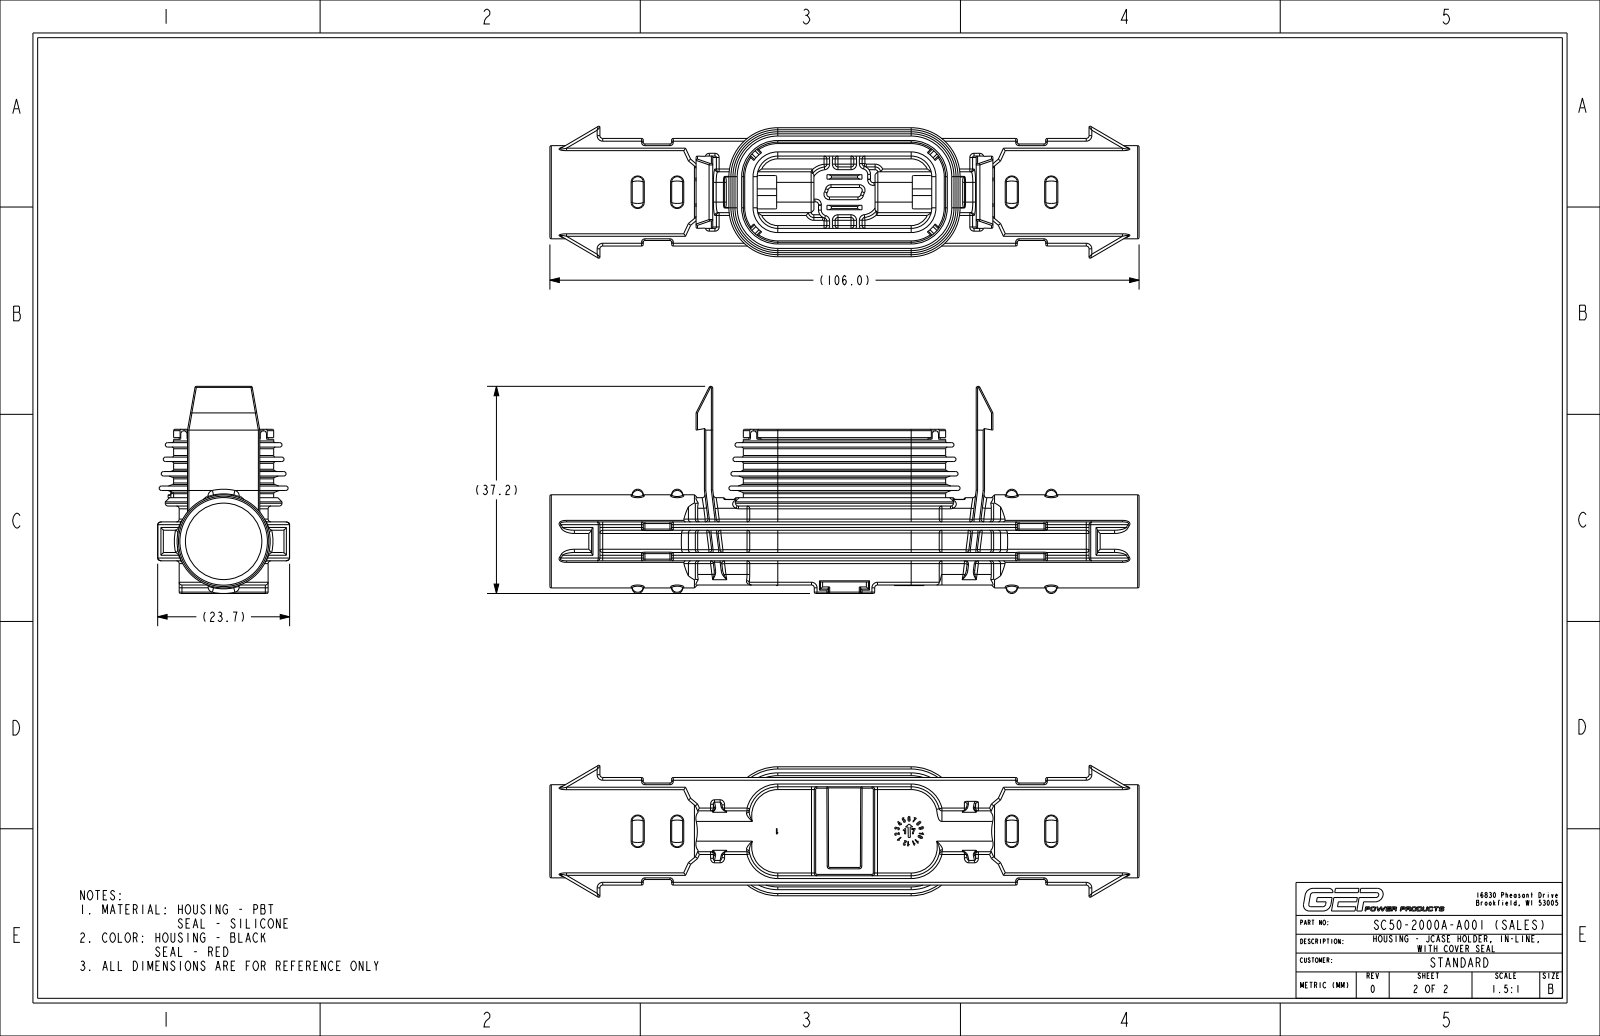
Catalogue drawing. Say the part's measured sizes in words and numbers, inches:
The part is named "PC26-2003A-B001_MOLD_SALES_NCF; PC26-2003A-B001_SALES_NCF_ASM; PC14-2002A-B002_NCF_INST; PC50-2000A-A001_SALES_NCF_ASM (+1 more)". Its 3-D file was written by "CREO PARAMETRIC BY PTC INC, 2017110 (CONFIG_CONTROL_DESIGN)". It is 2 solids with 2058 faces: 565 planar, 664 cylindrical and 829 other. Overall it measures 4.173 by 1.467 by 0.935 inches. Its volume is 1.307 cubic inches and its surface area 30.65 square inches. Round holes: 1 of diameter 0.541. Round bosses or shafts: 1 of diameter 0.659. Partial cylindrical surfaces (rounded edges, fillets, slot ends): 210 of radius 0.02, 73 of radius 0.012, 55 of radius 0.01, 24 of radius 0.008, 20 of radius 0.016, 8 of radius 0.009, 4 of radius 0.059, 4 of radius 0.075. The main face-to-face distances are 0.059, 0.571, 0.171, 0.388, 0.447, 0.217, 0.63, 0.512, 0.23, 0.102.
